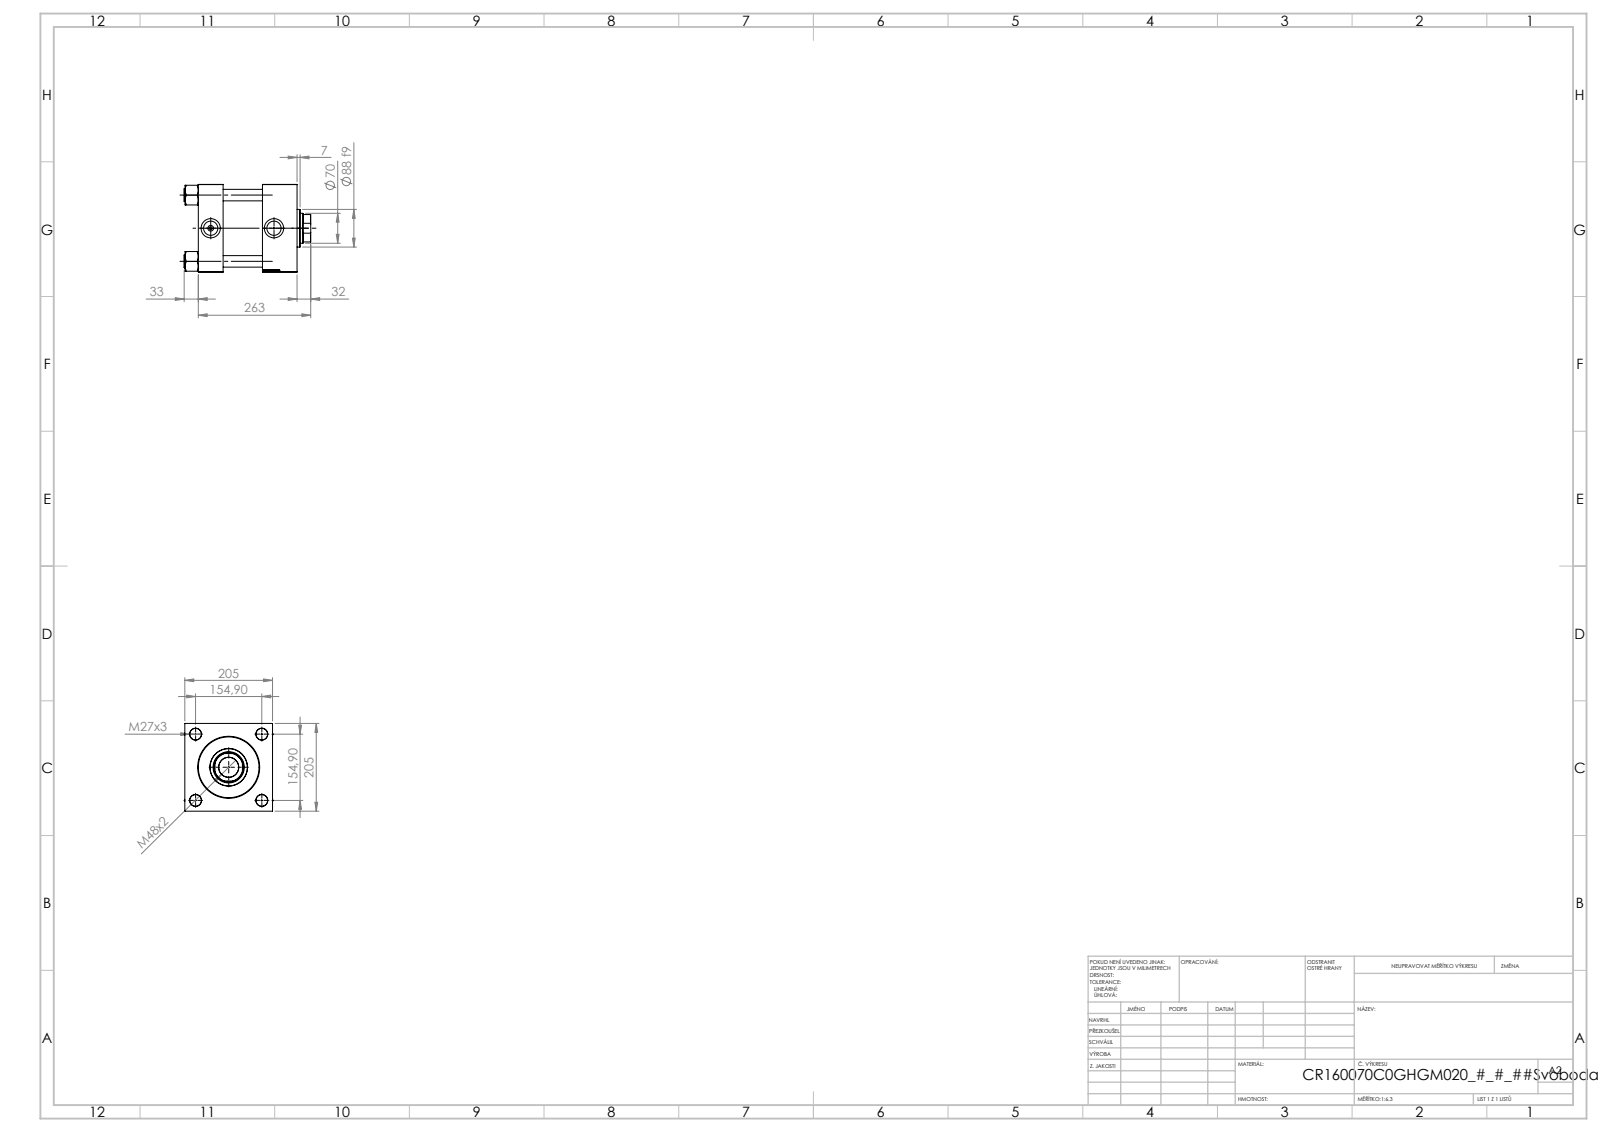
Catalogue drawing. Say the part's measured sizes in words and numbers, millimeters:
The part is named "NUT_M5_C; V215CR_C_TYCINKA; V215_VC_A; V215CR_C_Body (+1 more)". Its 3-D file was written by "SolidWorks 2019 (CONFIG_CONTROL_DESIGN)". It is 11 solids with 1196 faces: 574 planar, 86 cylindrical and 536 other. Overall it measures 296 by 208.14 by 205 millimeters. Its volume is 7 447 000 cubic millimeters and its surface area 694 274 square millimeters. Round holes: 4 of diameter 27, 2 of diameter 7, 2 of diameter 33.24, 2 of diameter 45, 1 of diameter 46.5, 1 of diameter 70, 1 of diameter 73, 1 of diameter 120, 1 of diameter 142, 1 of diameter 160. Round bosses or shafts: 4 of diameter 30, 1 of diameter 166, 1 of diameter 88. Partial cylindrical surfaces (rounded edges, fillets, slot ends): 1 of radius 34. The main face-to-face distances are 205, 58, 231, 173, 150, 92, 81, 202.3, 144.3, 52.3. The hole center spacings are 109.53, 154.9, 219.06, 148.
